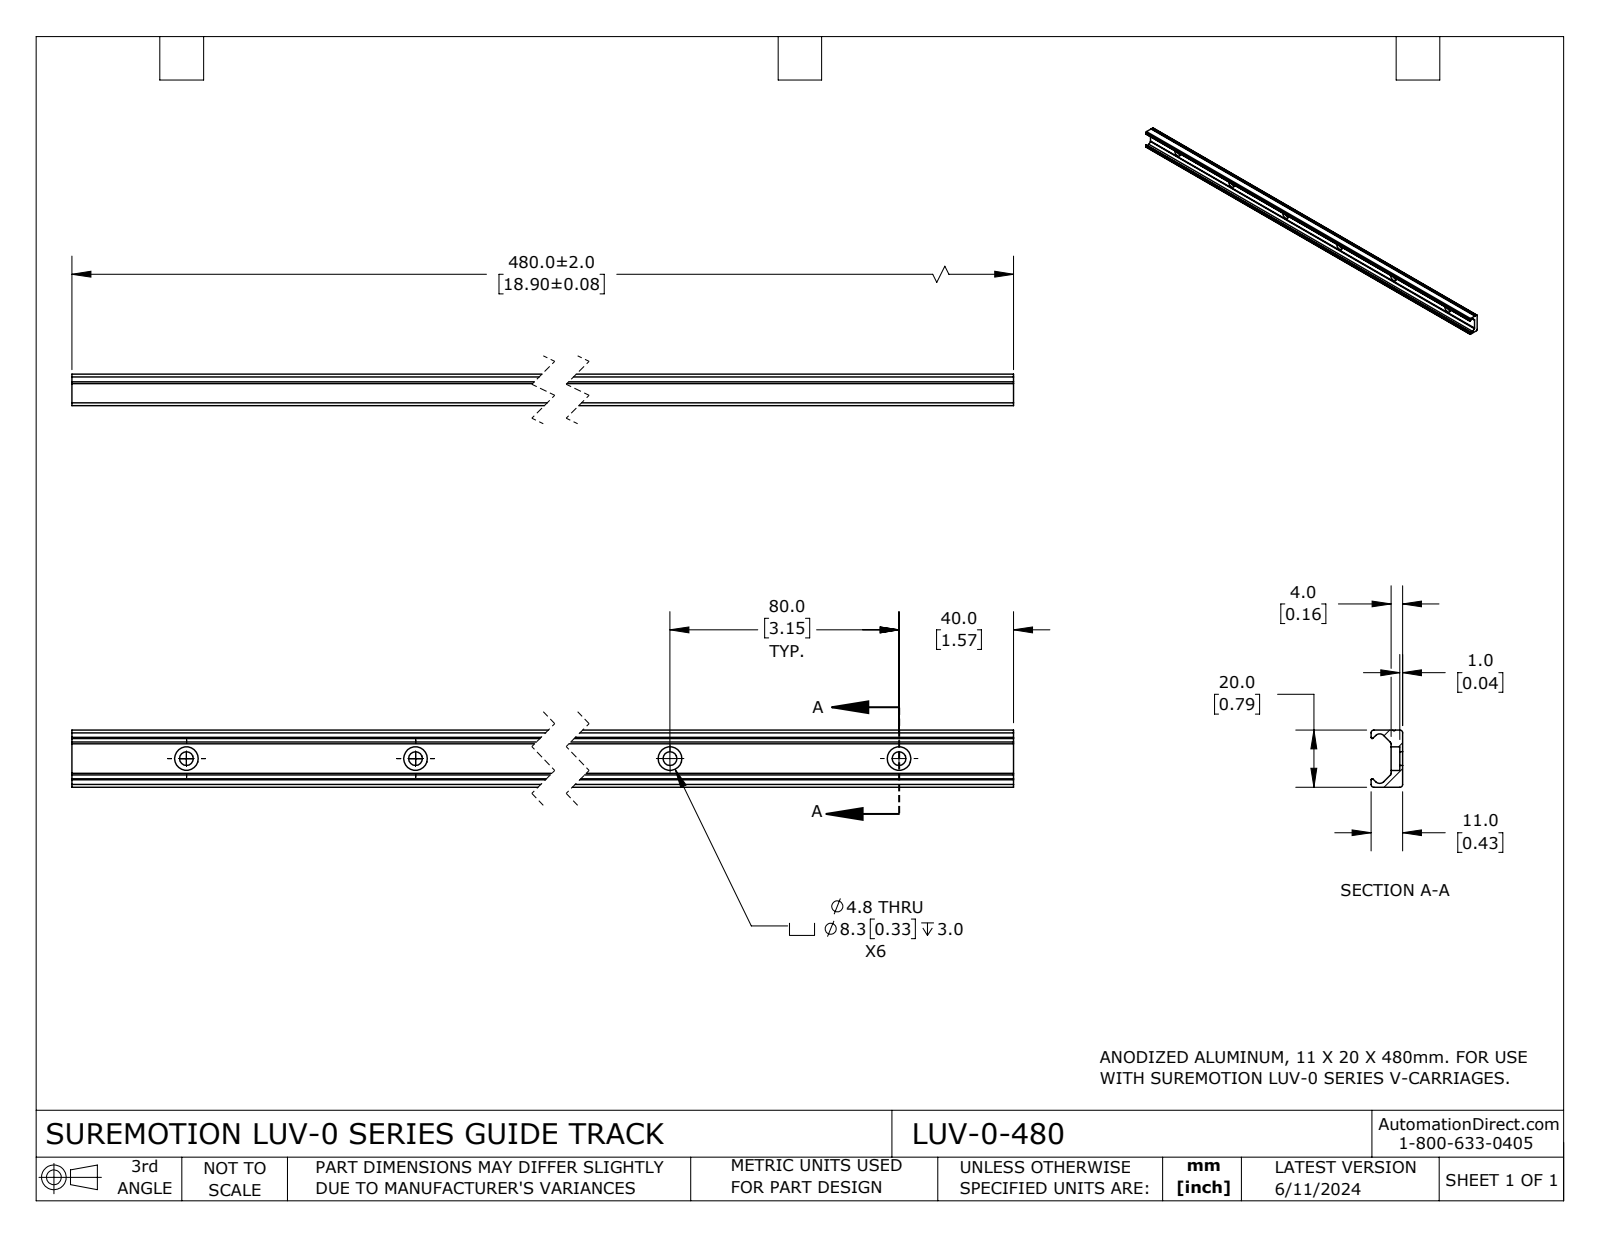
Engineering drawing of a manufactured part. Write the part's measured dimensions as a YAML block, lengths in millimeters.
part_name: "LUV-0-480"
step_written_by: "SolidWorks 2023 (CONFIG_CONTROL_DESIGN)"
units: millimeters
bodies: {solids: 1, faces: 56, planar: 19, cylindrical: 37, other: 0}
overall_size: [480, 19.99, 11]
volume: 52977
surface_area: 36462
round_holes:
  - {diameter: 4.8, count: 6}
  - {diameter: 8.26, count: 5}
  - {diameter: 8.25, count: 1}
partial_cylinders:
  - {radius: 0.99, count: 4}
  - {radius: 0.38, count: 2}
  - {radius: 0.4, count: 2}
  - {radius: 0.79, count: 2}
  - {radius: 1.98, count: 2}
  - {radius: 0.33, count: 1}
face_to_face_distances: [4.01, 20, 11, 6.99, 13.4, 1.01, 3, 9.99, 480]
hole_center_spacings: [80, 160, 240, 320, 400]
